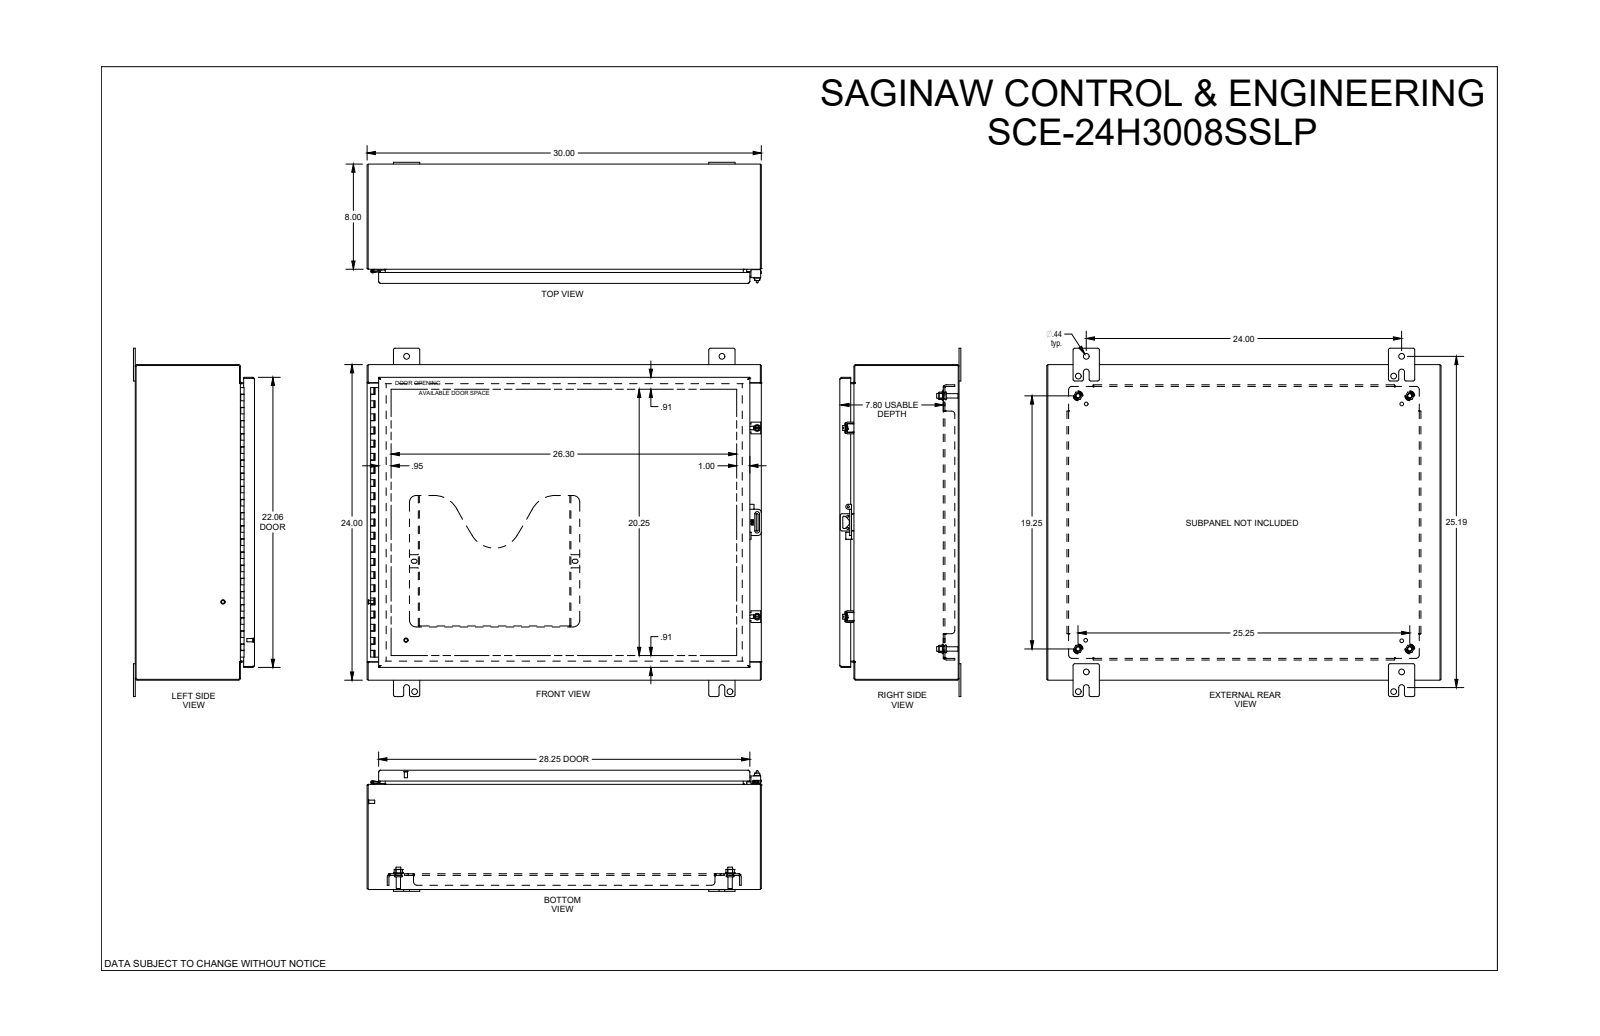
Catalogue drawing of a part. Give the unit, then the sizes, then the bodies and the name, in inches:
Units: inches
Overall size (bounding box): 30 × 26.5 × 9.208
Round holes (diameter × count): ⌀0.437 ×8, ⌀0.25 ×5, ⌀0.19 ×4, ⌀0.193 ×4, ⌀0.281 ×4, ⌀0.367 ×4, ⌀0.5 ×4, ⌀0.16 ×2, ⌀0.203 ×2, ⌀0.13 ×1, ⌀0.132 ×1
Round bosses / shafts (diameter × count): ⌀0.248 ×7, ⌀0.563 ×5, ⌀0.366 ×4, ⌀0.332 ×4, ⌀0.256 ×4, ⌀0.188 ×4, ⌀0.25 ×3, ⌀0.507 ×2
Partial cylindrical surfaces — rounded edges, fillets, slot ends (radius × count): R0.01 ×114, R0.015 ×36, R0.029 ×30, R0.03 ×27, R0.125 ×27, R0.06 ×25, R0.04 ×22, R0.07 ×14
Main face-to-face distances: 0.075, 8.998, 8.923, 0.075, 1.2, 7.873, 9.073, 8.998, 7.923, 1.125
Hole centre spacings: 24, 0.875, 33.941, 6.5, 18.641, 24.639, 30.884, 0.516
Bodies: 0 solids, 3192 faces (1285 planar, 670 cylindrical, 1237 other)
Part name (STEP PRODUCT): SCE-24H3008SSLP
STEP written by: SolidWorks 2019 (CONFIG_CONTROL_DESIGN)
